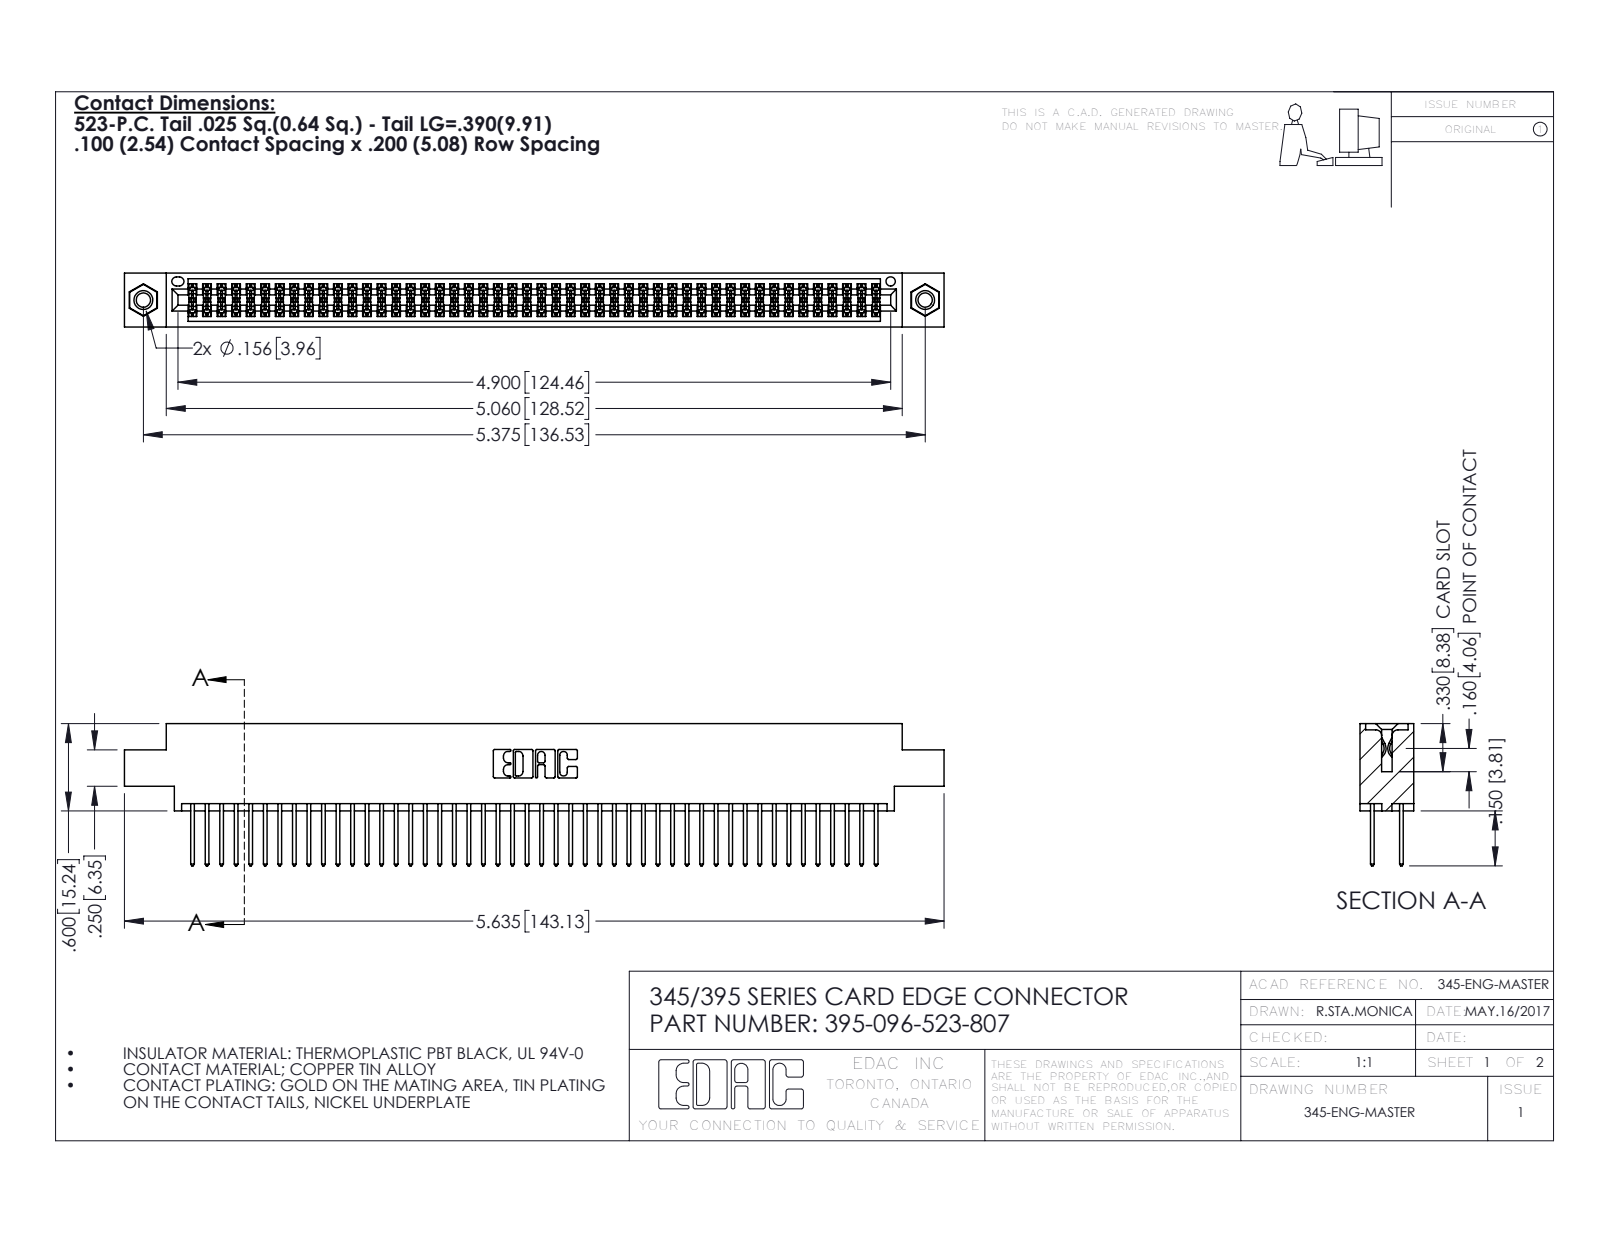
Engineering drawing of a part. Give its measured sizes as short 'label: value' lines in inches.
name: 345 Part_0.170 Offset - 0.156 Dia-TI; 345-250-001_345-250-005-103; 395-096-523-807; 345-292-001_345-293-123
written by: SolidWorks 2016 (CONFIG_CONTROL_DESIGN)
unit: in
bodies: 99 solids, 4990 faces (3284 planar, 1690 cylindrical, 16 other)
size: 5.635 × 0.977 × 0.37
volume: 0.856 in³; area: 33.96 in²
holes: 2× ⌀0.098, 2× ⌀0.125, 2× ⌀0.156, 1× ⌀0.064
bosses: 2× ⌀0.155
rounds: 144× R0.006, 96× R0.01, 22× R0.01, 6× R0.007, 6× R0.031, 3× R0.026, 2× R0.014, 2× R0.019
face distances: 0.072, 0.298, 0.2, 0.098, 0.272, 0.025, 0.37, 0.225, 0.175, 0.149
hole spacings: 0.27, 5.139, 5.375
